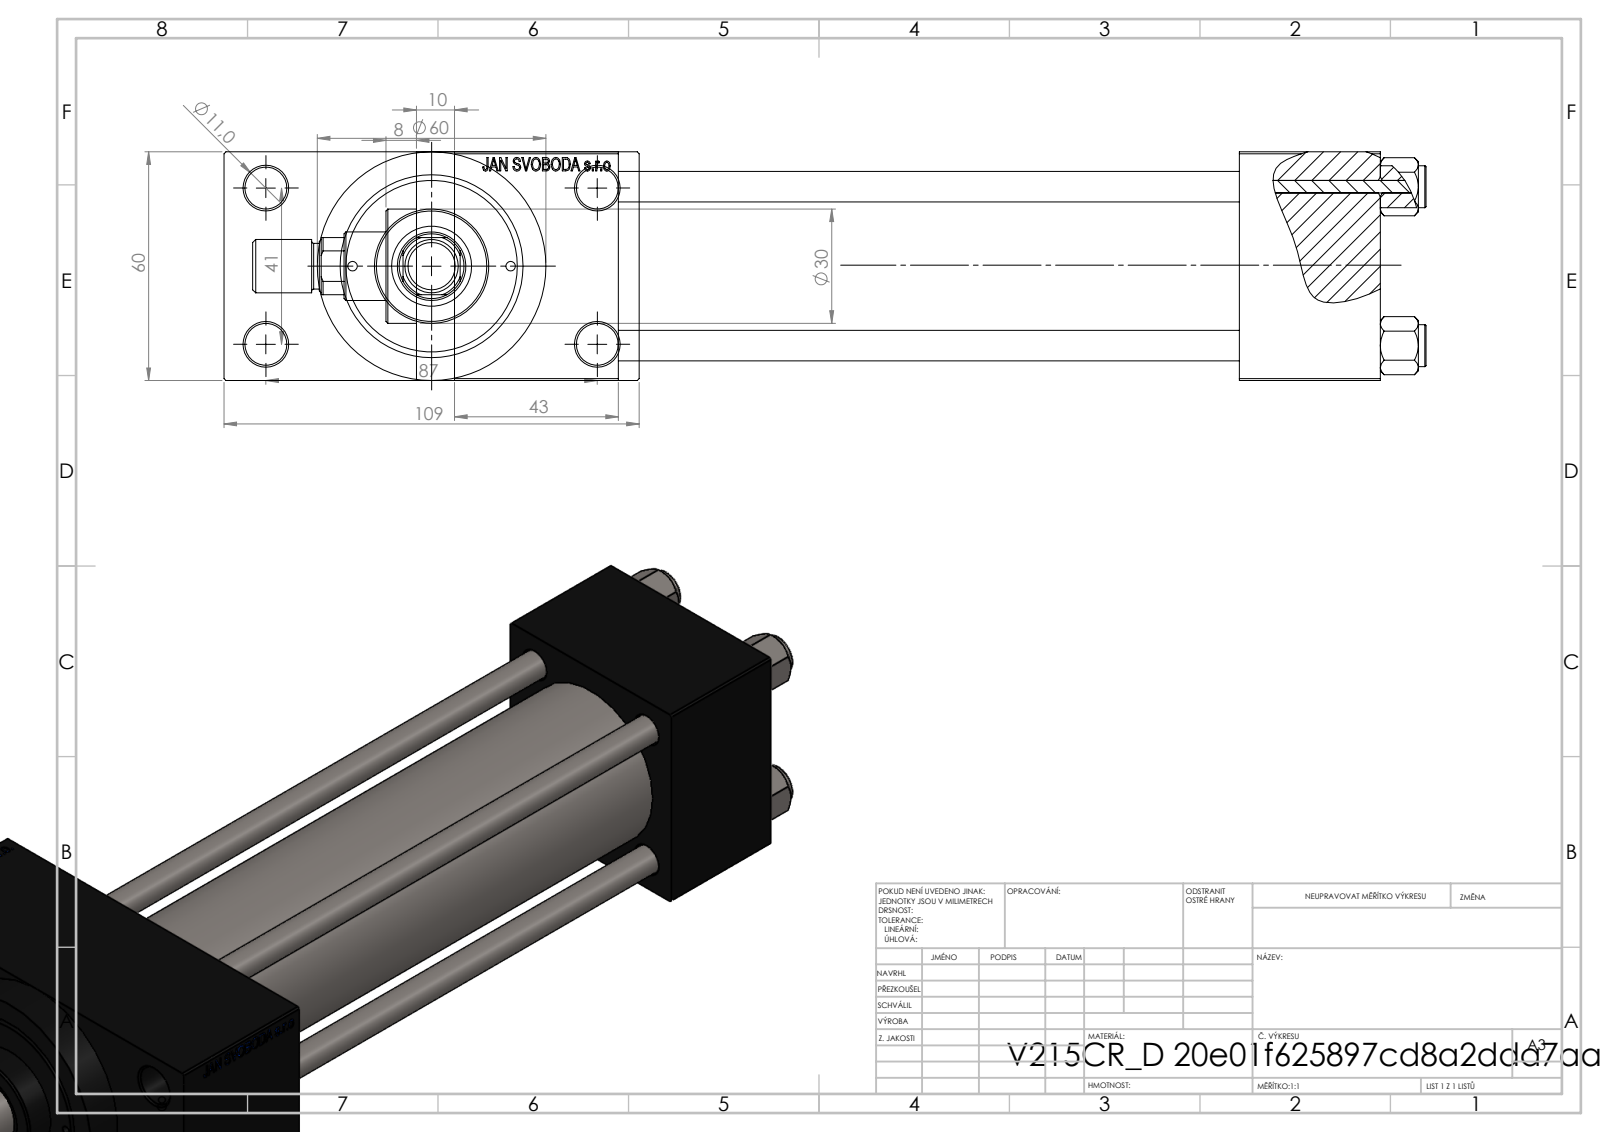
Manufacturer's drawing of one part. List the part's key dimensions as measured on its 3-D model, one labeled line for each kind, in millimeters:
Part name (STEP PRODUCT): V215CR_VCP_D; ROD_END_AH; V215CR_D_Body; V215CR_D_TYCINKA (+2 more)
STEP written by: SolidWorks 2019 (CONFIG_CONTROL_DESIGN)
Units: millimetres
Bodies: 12 solids, 1127 faces (504 planar, 97 cylindrical, 526 other)
Overall size (bounding box): 308 × 109 × 60
Volume: 610 628 mm³ · Surface area: 167 209 mm²
Round holes (diameter × count): ⌀8 ×4, ⌀11 ×4, ⌀2.5 ×2, ⌀7 ×2, ⌀16.66 ×2, ⌀24 ×2, ⌀8.5 ×1, ⌀18 ×1, ⌀21 ×1, ⌀31 ×1, ⌀40 ×1, ⌀45 ×1
Round bosses / shafts (diameter × count): ⌀11 ×4, ⌀60 ×1, ⌀46 ×1, ⌀30 ×1, ⌀14 ×1, ⌀12 ×1
Partial cylindrical surfaces — rounded edges, fillets, slot ends (radius × count): R8.5 ×1
Main face-to-face distances: 60, 24.5, 84.5, 163, 37, 200, 43, 243, 206, 109
Hole centre spacings: 20.85, 22.65, 29.49, 30.62, 41.7, 46.53, 47.15, 48.09
